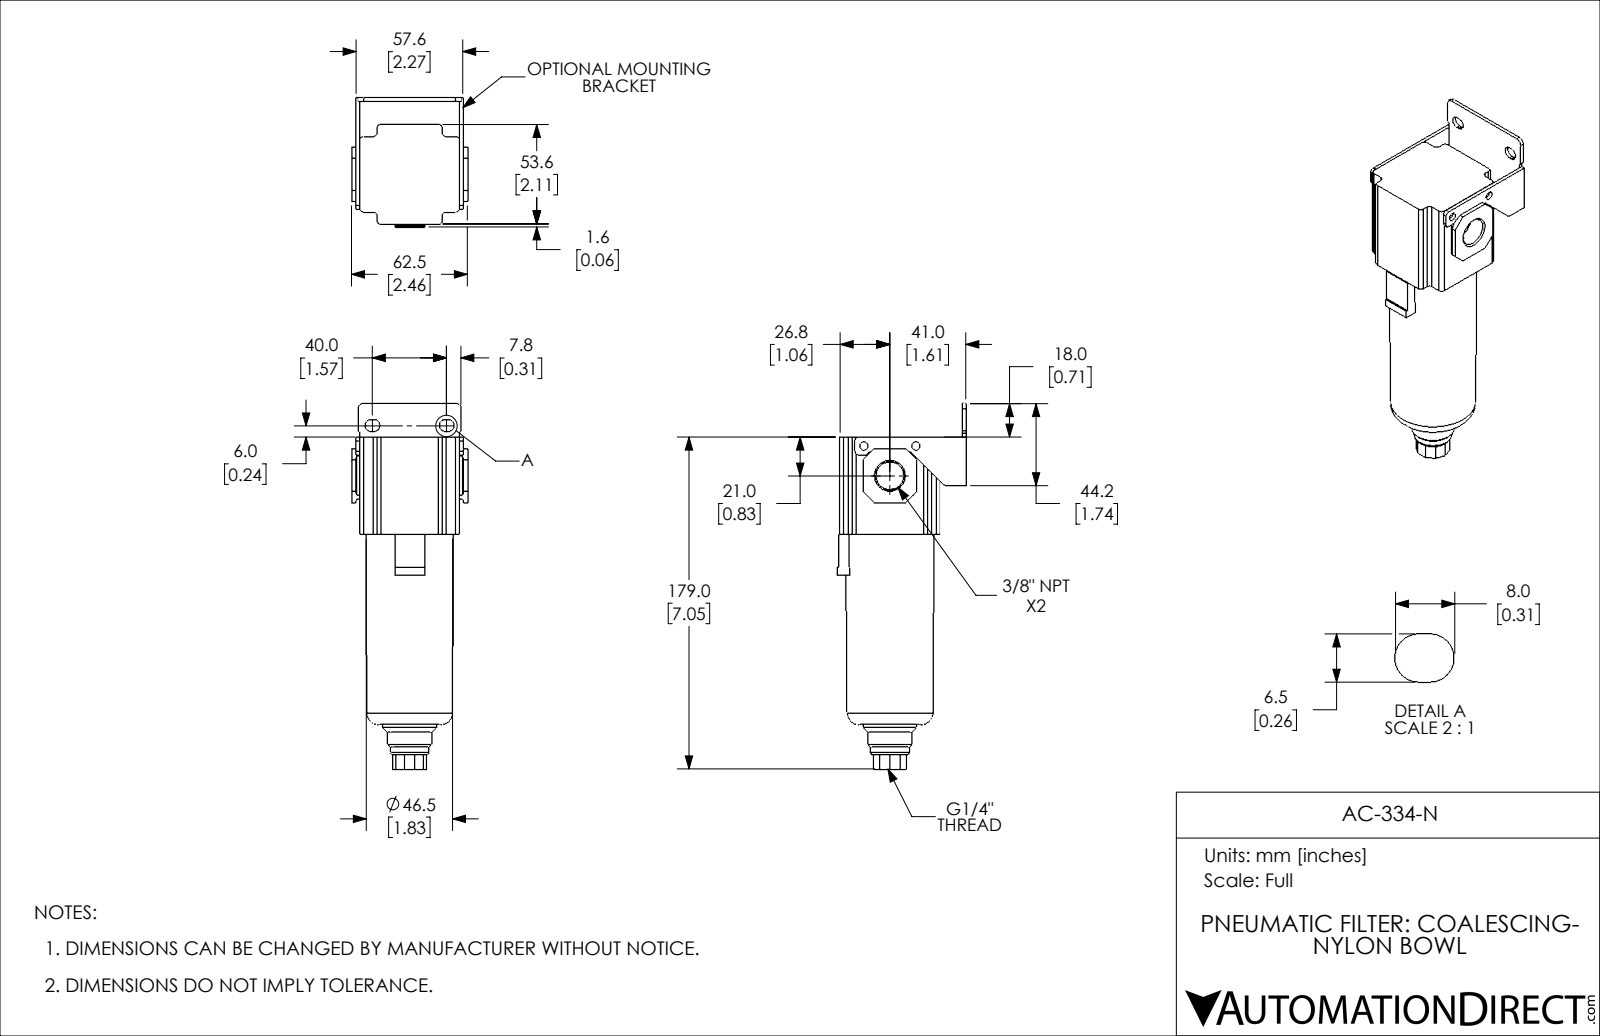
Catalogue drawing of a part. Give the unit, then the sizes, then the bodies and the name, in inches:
Units: inches
Overall size (bounding box): 7.756 × 2.733 × 2.461
Round holes (diameter × count): ⌀0.177 ×2, ⌀0.451 ×1, ⌀0.589 ×1
Round bosses / shafts (diameter × count): ⌀1.102 ×1, ⌀0.906 ×1, ⌀0.787 ×1
Partial cylindrical surfaces — rounded edges, fillets, slot ends (radius × count): R0.079 ×15, R0.128 ×4, R0.039 ×2, R0.118 ×2
Main face-to-face distances: 0.079, 2.11, 2.189, 0.559, 2.669, 0.48, 2.591, 2.067, 0.258, 1.852
Hole centre spacings: 0.837, 1.102
Volume: 19.92 in³ · Surface area: 65.58 in²
Bodies: 1 solid, 173 faces (109 planar, 48 cylindrical, 16 other)
Part name (STEP PRODUCT): AC-334-N
STEP written by: SolidWorks 2018 (AUTOMOTIVE_DESIGN)
